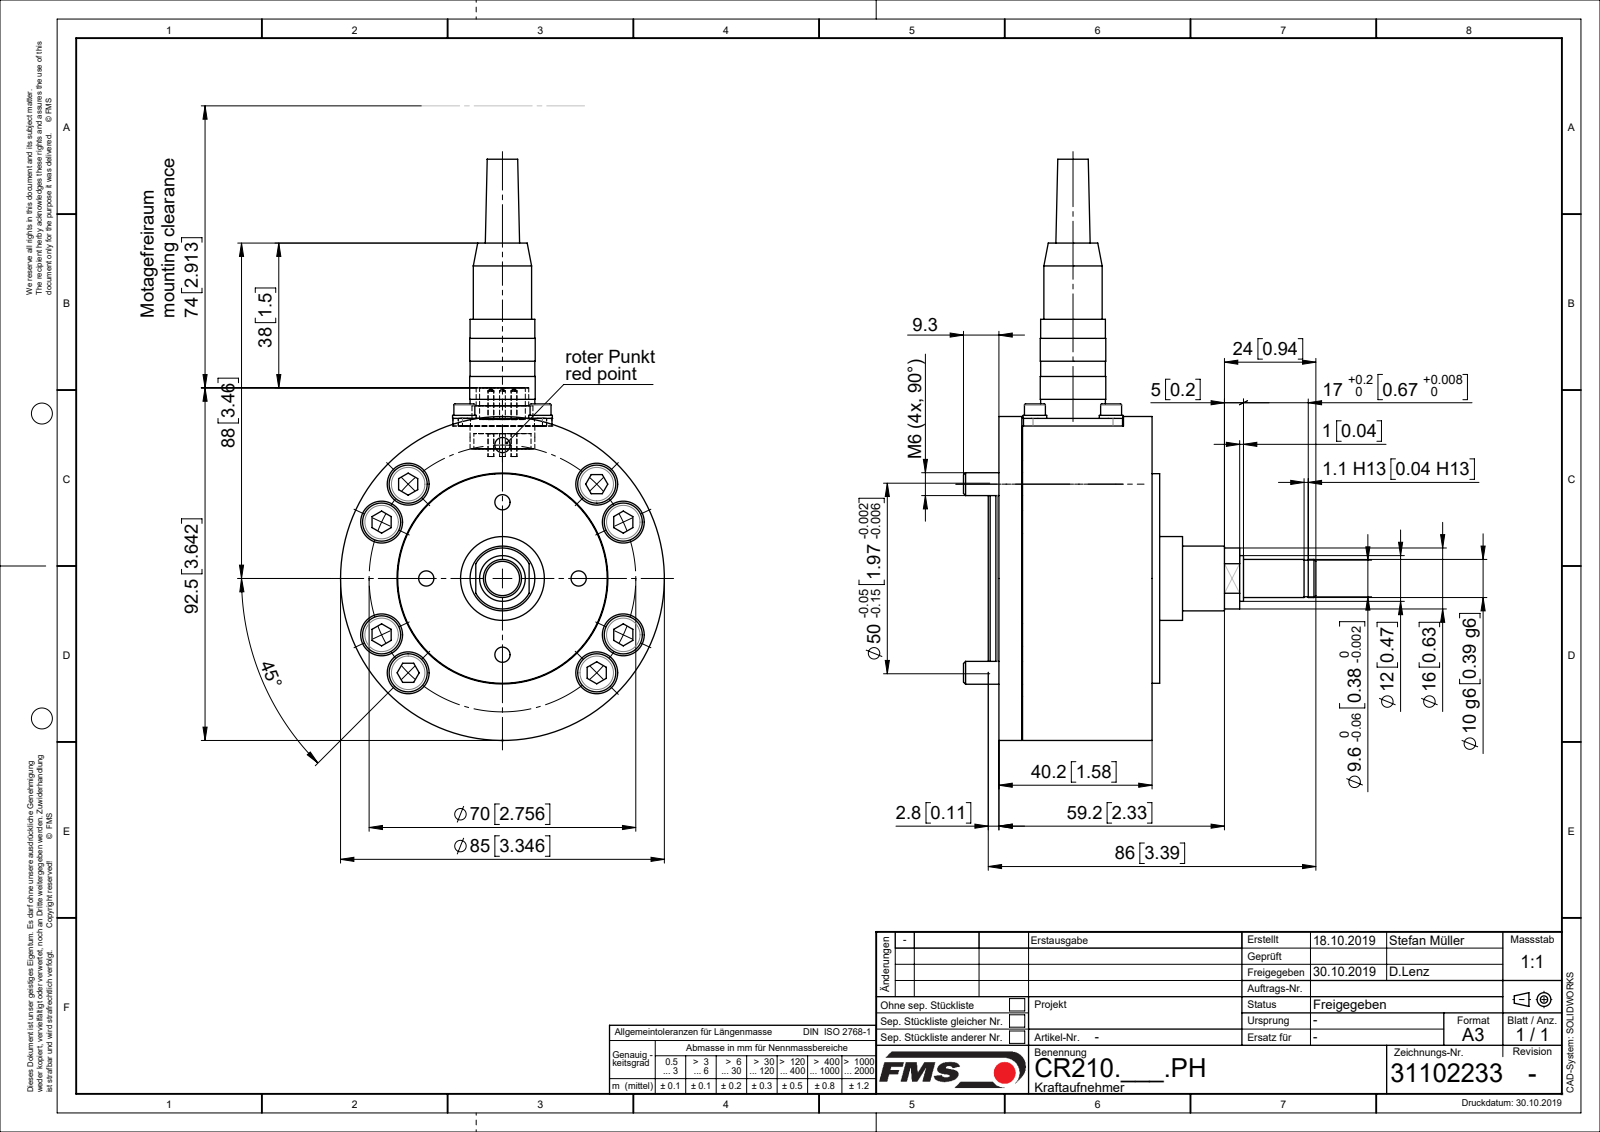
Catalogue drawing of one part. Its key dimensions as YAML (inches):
part_name: "31102233_STP; C0709081; C0612056; C0709072 (+8 more)"
step_written_by: "Mechanical Desktop 2009 (CONFIG_CONTROL_DESIGN)"
units: inches
bodies: {solids: 26, faces: 520, planar: 179, cylindrical: 243, other: 98}
overall_size: [6.004, 3.642, 3.346]
volume: 14.07
surface_area: 113.2
round_holes:
  - {diameter: 0.256, count: 8}
  - {diameter: 0.433, count: 8}
  - {diameter: 0.102, count: 4}
  - {diameter: 0.126, count: 4}
  - {diameter: 0.157, count: 4}
  - {diameter: 0.203, count: 4}
  - {diameter: 0.276, count: 4}
  - {diameter: 0.281, count: 1}
  - {diameter: 0.42, count: 1}
  - {diameter: 0.472, count: 1}
  - {diameter: 0.591, count: 1}
  - {diameter: 0.709, count: 1}
round_bosses_or_shafts:
  - {diameter: 0.394, count: 9}
  - {diameter: 0.236, count: 8}
  - {diameter: 0.059, count: 5}
  - {diameter: 0.244, count: 4}
  - {diameter: 0.217, count: 4}
  - {diameter: 0.197, count: 4}
  - {diameter: 0.118, count: 4}
  - {diameter: 0.669, count: 2}
partial_cylinders:
  - {radius: 0.098, count: 4}
  - {radius: 0.197, count: 2}
  - {radius: 0.315, count: 1}
face_to_face_distances: [0.236, 0.248, 0.079, 0.106, 1.339, 1.587, 1.35, 1.772, 0.118, 1.665]
hole_center_spacings: [0.787, 0.992, 1.378, 2.013, 1.113, 0.479, 0.557, 0.743]
